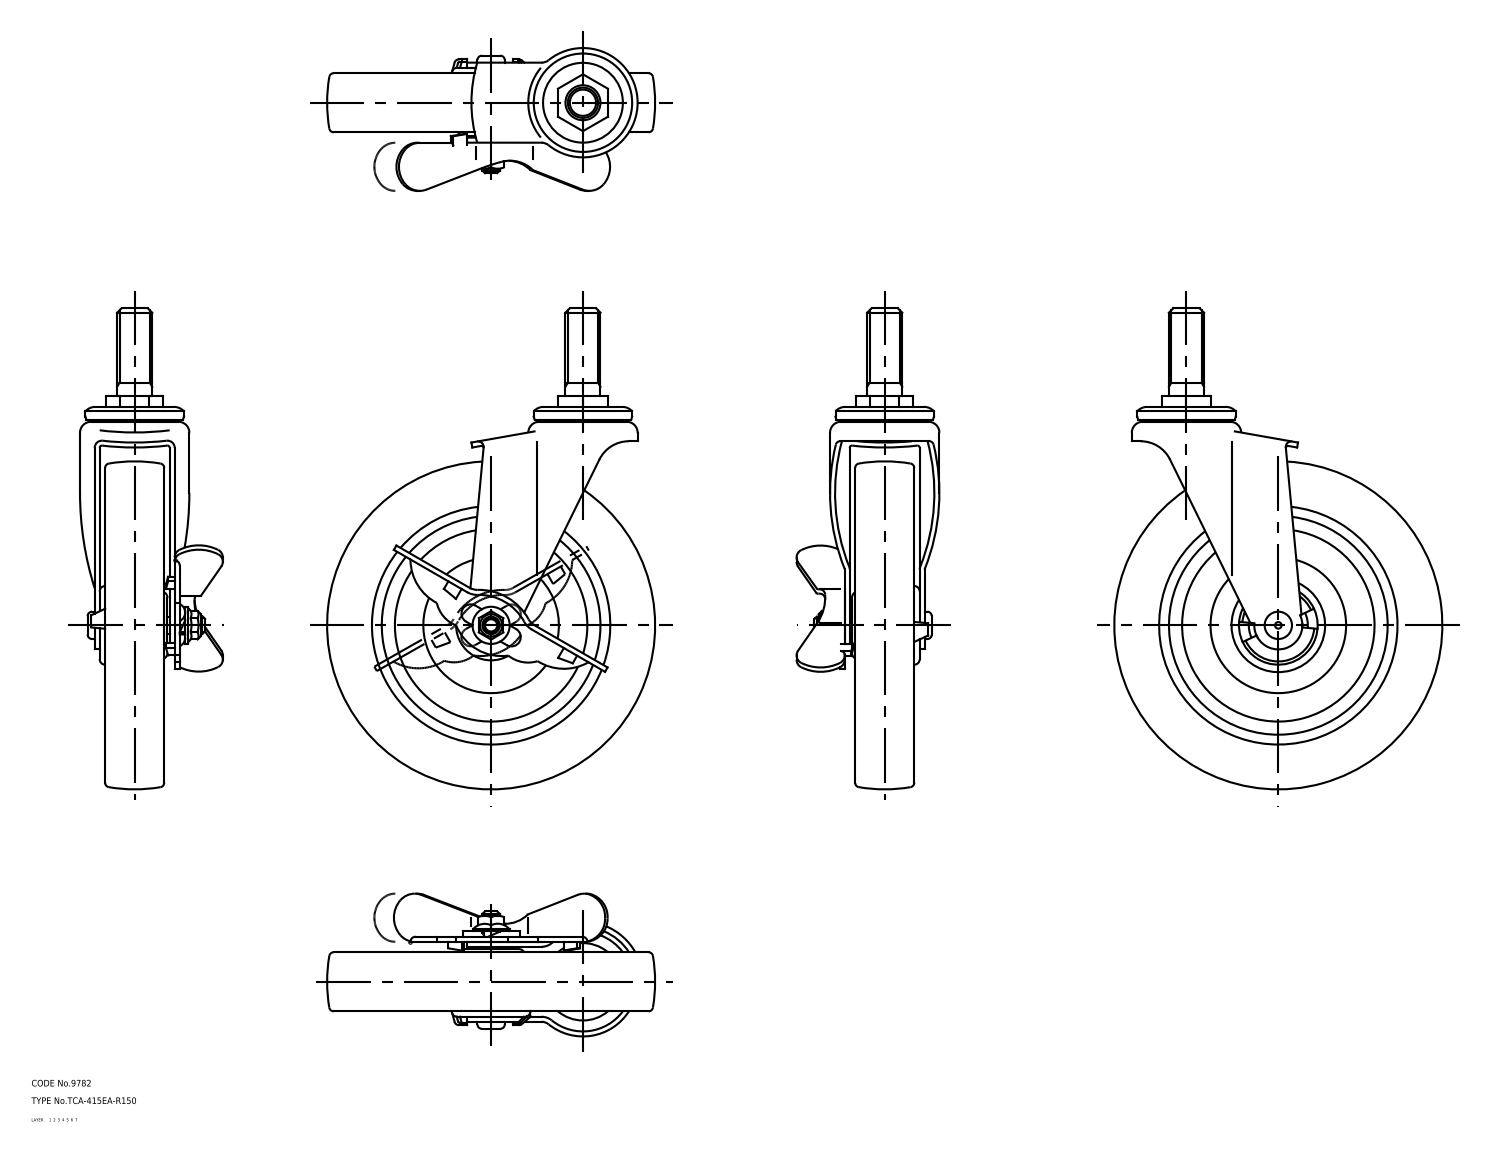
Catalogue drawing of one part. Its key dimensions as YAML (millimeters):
part_name: "wheel; mounting plate; main shaft; lever (+2 more)"
step_written_by: "CADfix (AUTOMOTIVE_DESIGN)"
units: millimeters
bodies: {solids: 6, faces: 351, planar: 0, cylindrical: 0, other: 351}
overall_size: [220, 150, 65.3]
volume: 520760
surface_area: 92270
